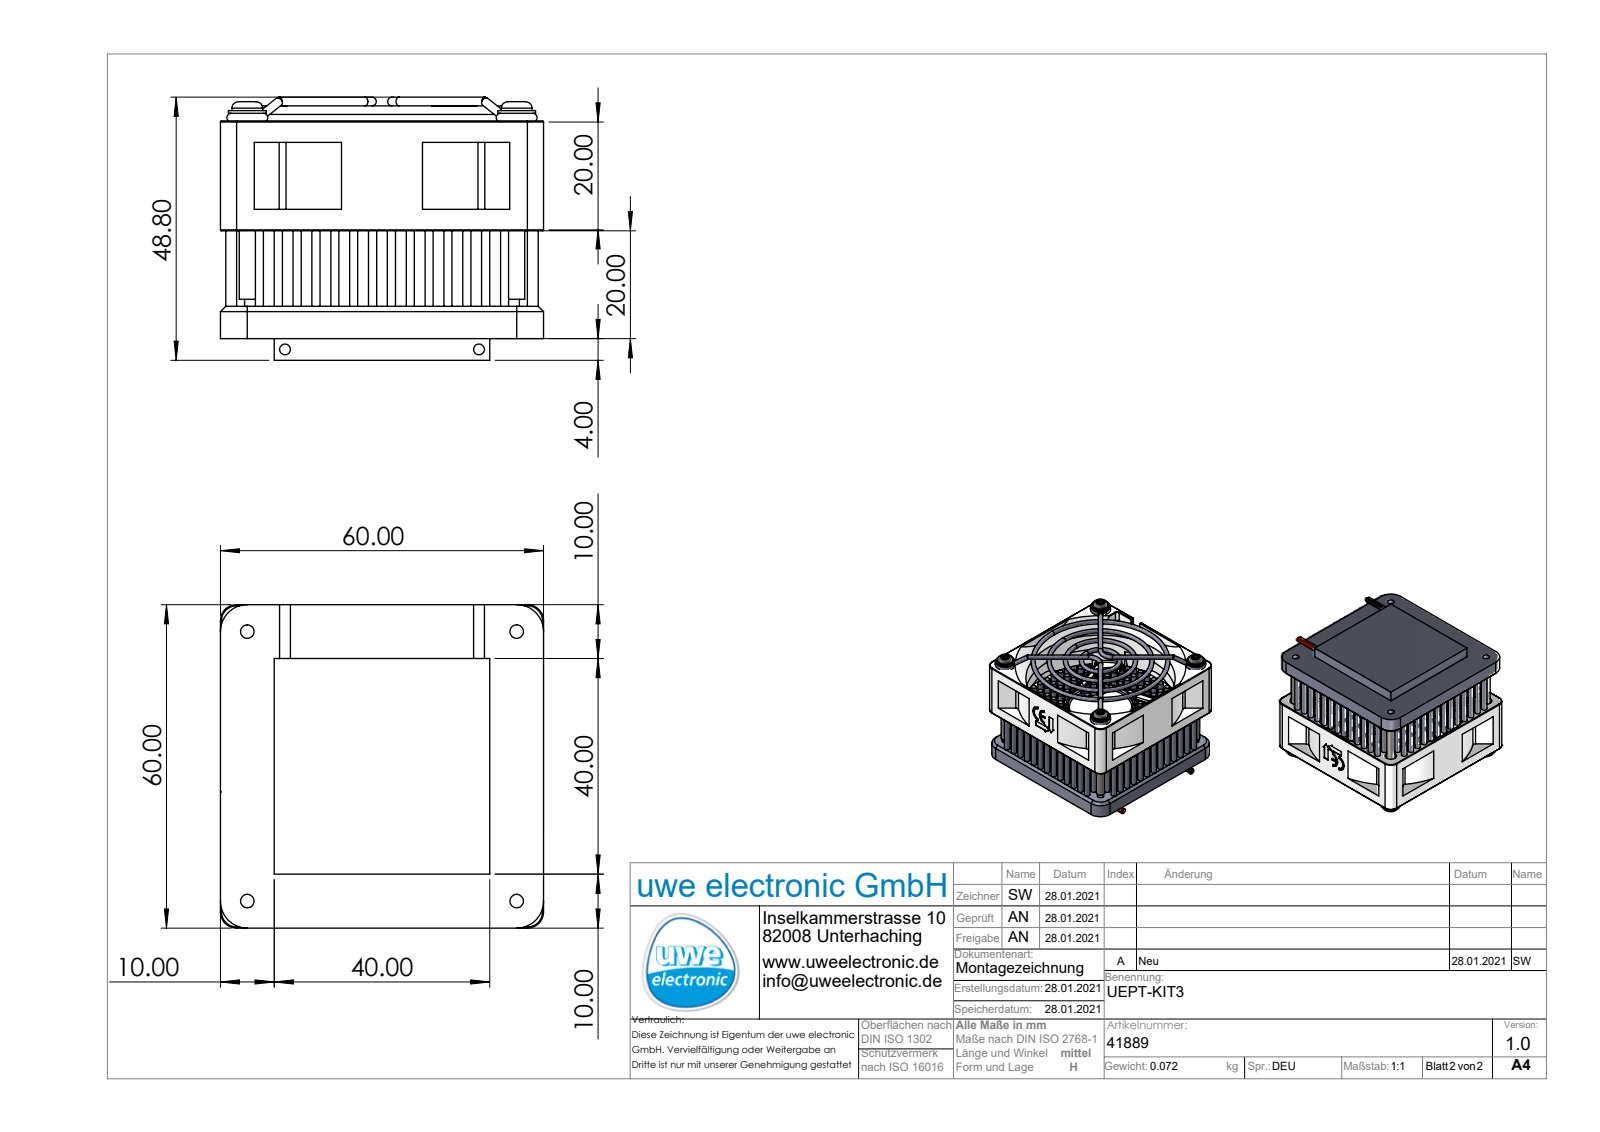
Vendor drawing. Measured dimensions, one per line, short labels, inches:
name: UEPT-EVAKIT-3; Lüfterschutzgitter 60x60; 41731; Scheibe_DIN125A_Scheibe_D3,2 (+3 more)
written by: SolidWorks 2020 (AUTOMOTIVE_DESIGN)
unit: in
bodies: 21 solids, 1563 faces (655 planar, 766 cylindrical, 142 other)
size: 2.362 × 2.362 × 1.921
volume: 3.597 in³; area: 87.87 in²
holes: 4× ⌀0.098, 4× ⌀0.126, 4× ⌀0.169, 1× ⌀0.866, 1× ⌀0.953, 1× ⌀2.181
bosses: 275× ⌀0.079, 8× ⌀0.063, 4× ⌀0.276, 4× ⌀0.224, 4× ⌀0.118, 1× ⌀1
rounds: 27× R0.039, 22× R0.02, 20× R0.008, 7× R0.118, 6× R0.059, 5× R0.012, 5× R1.181, 4× R0.197
face distances: 0.236, 0.394, 0.157, 0.945, 2.362, 0.787, 0.551, 1.969, 1.591, 0.646
hole spacings: 1.392, 1.969, 2.784
